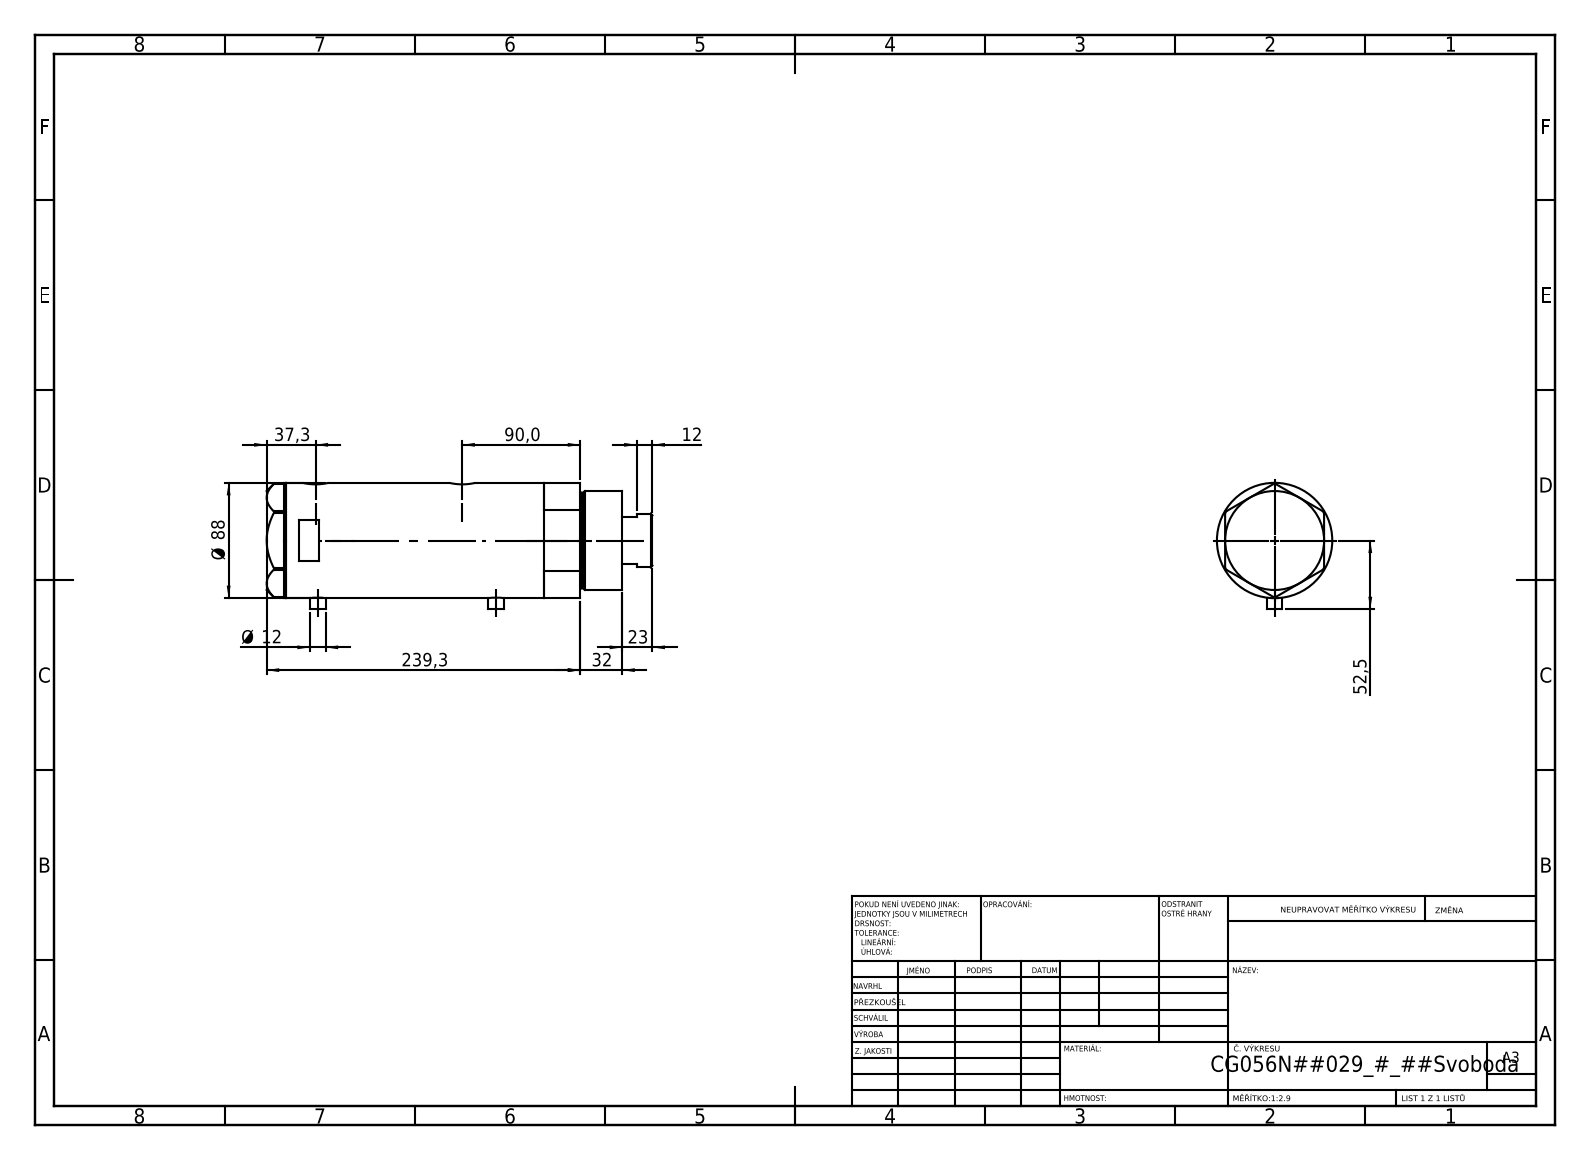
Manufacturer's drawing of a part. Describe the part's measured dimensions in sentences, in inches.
The part is named "V270CG_BACK; V270CG_FRONT; V270CG_VC; V270CG_MIDDLE". Its 3-D file was written by "SolidWorks 2019 (CONFIG_CONTROL_DESIGN)". It is 4 solids with 126 faces: 53 planar, 53 cylindrical and 20 other. Overall it measures 11.587 by 3.799 by 3.465 inches. Its volume is 94.95 cubic inches and its surface area 345.4 square inches. Round holes: 2 of diameter 0.197, 2 of diameter 0.492, 2 of diameter 0.518, 2 of diameter 0.787, 1 of diameter 0.571, 1 of diameter 1.654, 1 of diameter 1.713, 1 of diameter 2.205, 1 of diameter 2.362, 1 of diameter 3.15. Round bosses or shafts: 2 of diameter 0.472, 1 of diameter 3.465, 1 of diameter 2.953, 1 of diameter 2.874, 1 of diameter 1.614. The main face-to-face distances are 5.291, 1.024, 4.268, 0.591, 1.614, 5.882, 10.091, 10.681, 9.067, 4.799. The hole center spacings are 0.067, 1.016, 4.343, 4.409, 5.358, 5.425.
